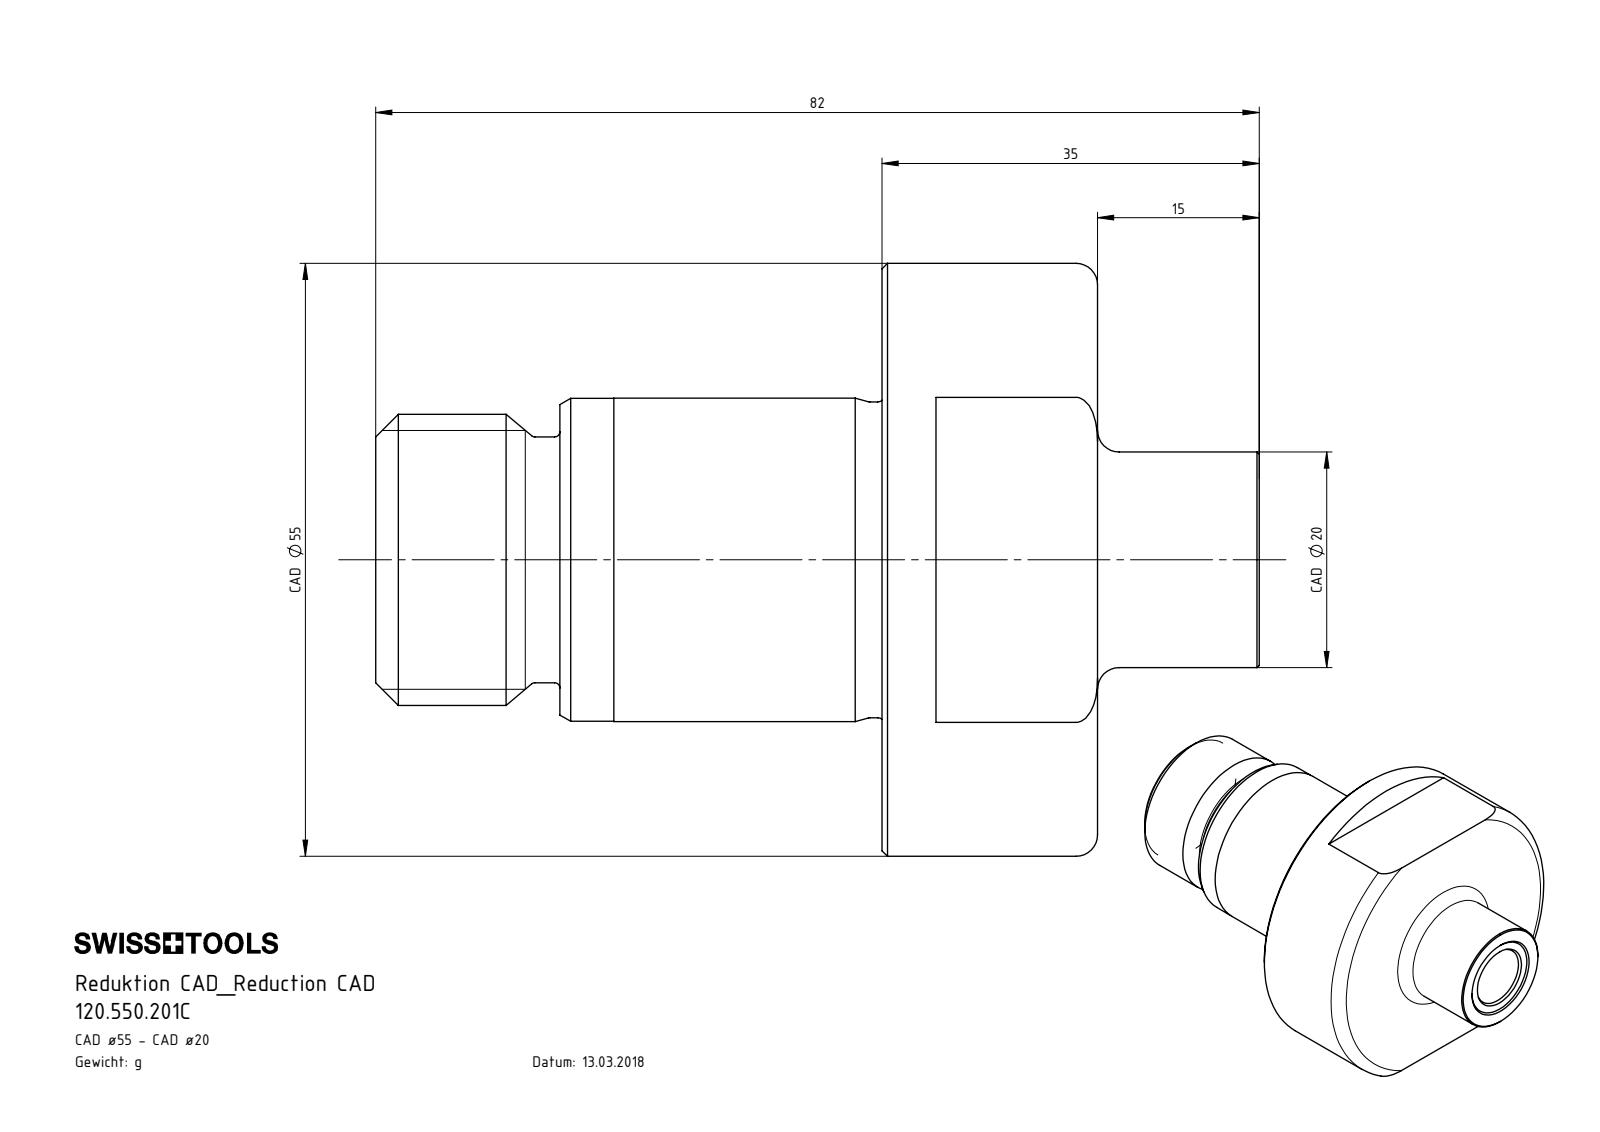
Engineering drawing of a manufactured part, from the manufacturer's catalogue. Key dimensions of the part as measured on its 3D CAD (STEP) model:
Part name (STEP PRODUCT): 120.550.201C
STEP written by: SolidWorks 2017 (CONFIG_CONTROL_DESIGN)
Units: millimetres
Bodies: 1 solid, 73 faces (12 planar, 20 cylindrical, 41 other)
Overall size (bounding box): 82 × 55 × 55
Volume: 74 273 mm³ · Surface area: 15 330 mm²
Round holes (diameter × count): ⌀8.5 ×1, ⌀11 ×1, ⌀11.5 ×1
Round bosses / shafts (diameter × count): ⌀55 ×1, ⌀30 ×1, ⌀29.95 ×1, ⌀29.3 ×1, ⌀27 ×1, ⌀22.8 ×1, ⌀20 ×1
Main face-to-face distances: 20, 46, 47, 67, 15, 29.9, 17.1, 49.9, 5, 52
